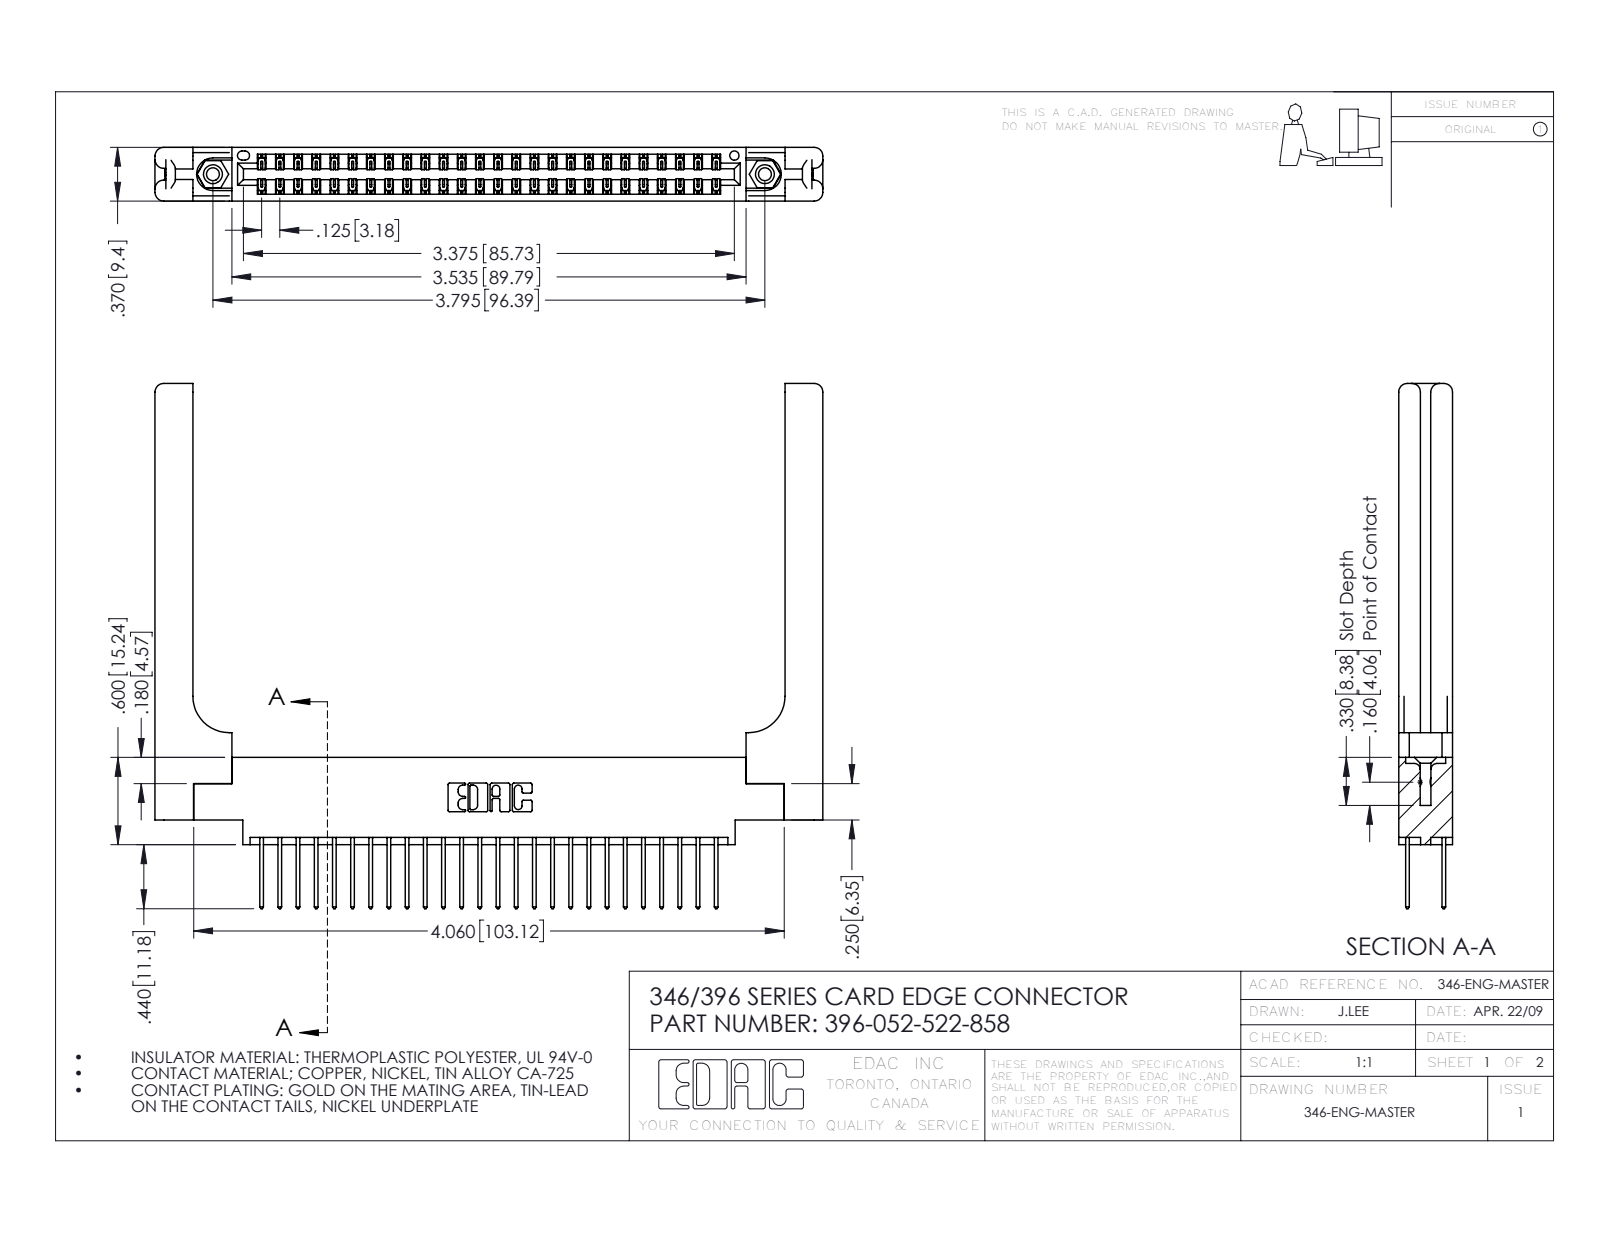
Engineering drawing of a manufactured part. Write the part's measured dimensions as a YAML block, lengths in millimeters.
part_name: "346-220-058_345-220-058; 396-052-522-858; 345-250-001_345-250-001-102; 346 Part_0.170 Offset - 0.156 Dia-TH (+1 more)"
step_written_by: "SolidWorks 2016 (CONFIG_CONTROL_DESIGN)"
units: millimeters
bodies: {solids: 57, faces: 3086, planar: 2048, cylindrical: 978, other: 60}
overall_size: [116.6, 91.7, 9.4]
volume: 18710
surface_area: 20950
round_holes:
  - {diameter: 2.3, count: 2}
  - {diameter: 3.2, count: 2}
  - {diameter: 4, count: 2}
  - {diameter: 1.6, count: 1}
round_bosses_or_shafts:
  - {diameter: 3.9, count: 2}
partial_cylinders:
  - {radius: 0.2, count: 78}
  - {radius: 0.3, count: 52}
  - {radius: 0.3, count: 22}
  - {radius: 1.5, count: 16}
  - {radius: 0.2, count: 6}
  - {radius: 0.8, count: 6}
  - {radius: 0.7, count: 3}
  - {radius: 0.4, count: 2}
face_to_face_distances: [9.4, 1.8, 1.2, 8.2, 6.4, 3.8, 3.8, 0.6, 7.6, 7]
hole_center_spacings: [6.2, 91.1, 96.4]
